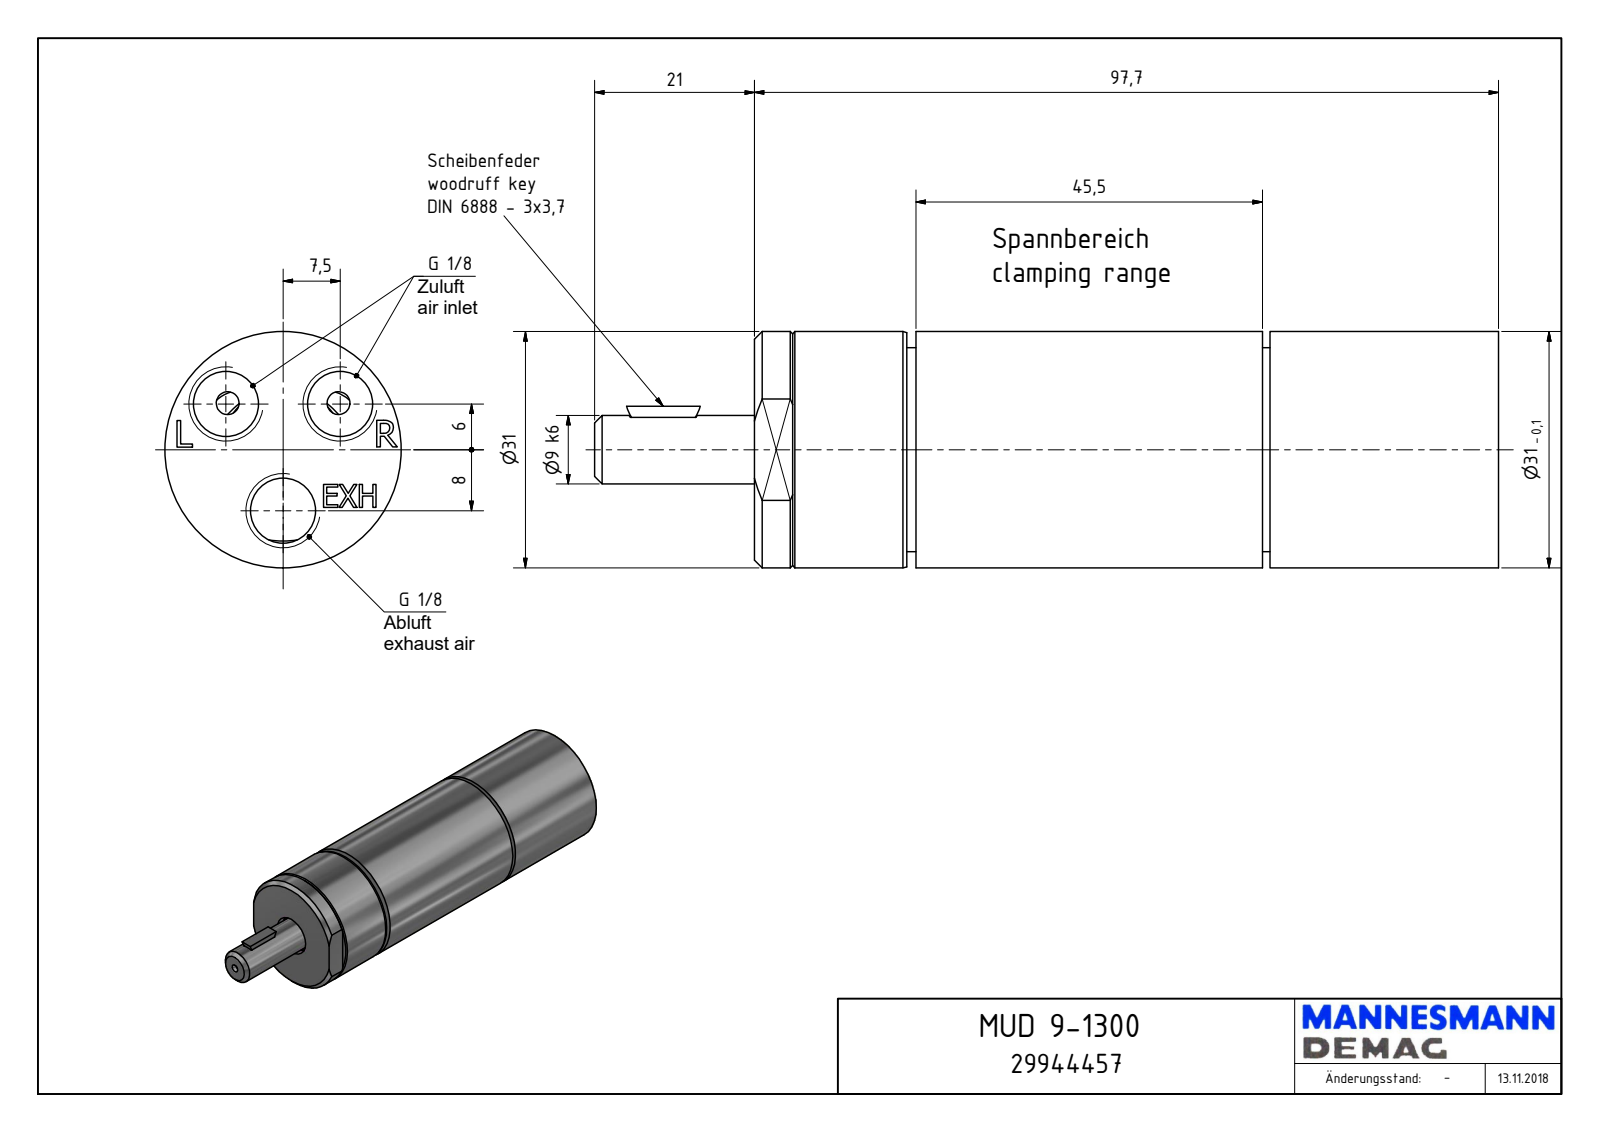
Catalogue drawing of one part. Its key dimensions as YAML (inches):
part_name: "MUD 9-1300_29944457"
step_written_by: "Autodesk Inventor 2018 (AUTOMOTIVE_DESIGN)"
units: inches
bodies: {solids: 1, faces: 148, planar: 92, cylindrical: 28, other: 28}
overall_size: [4.673, 1.22, 1.22]
volume: 4.402
surface_area: 22.46
round_holes:
  - {diameter: 0.337, count: 3}
  - {diameter: 0.039, count: 1}
  - {diameter: 0.408, count: 1}
  - {diameter: 0.413, count: 1}
  - {diameter: 0.63, count: 1}
  - {diameter: 1.154, count: 1}
round_bosses_or_shafts:
  - {diameter: 1.22, count: 1}
  - {diameter: 1.102, count: 1}
  - {diameter: 1.054, count: 1}
  - {diameter: 0.354, count: 1}
partial_cylinders:
  - {radius: 0.157, count: 2}
  - {radius: 0.197, count: 1}
  - {radius: 0.207, count: 1}
  - {radius: 0.437, count: 1}
  - {radius: 0.472, count: 1}
face_to_face_distances: [3.846, 0.835, 3.012, 2.626, 1.791, 1.22, 2.665, 1.831, 0.039, 1.181]
hole_center_spacings: [0.378, 0.625, 0.315, 0.591]
